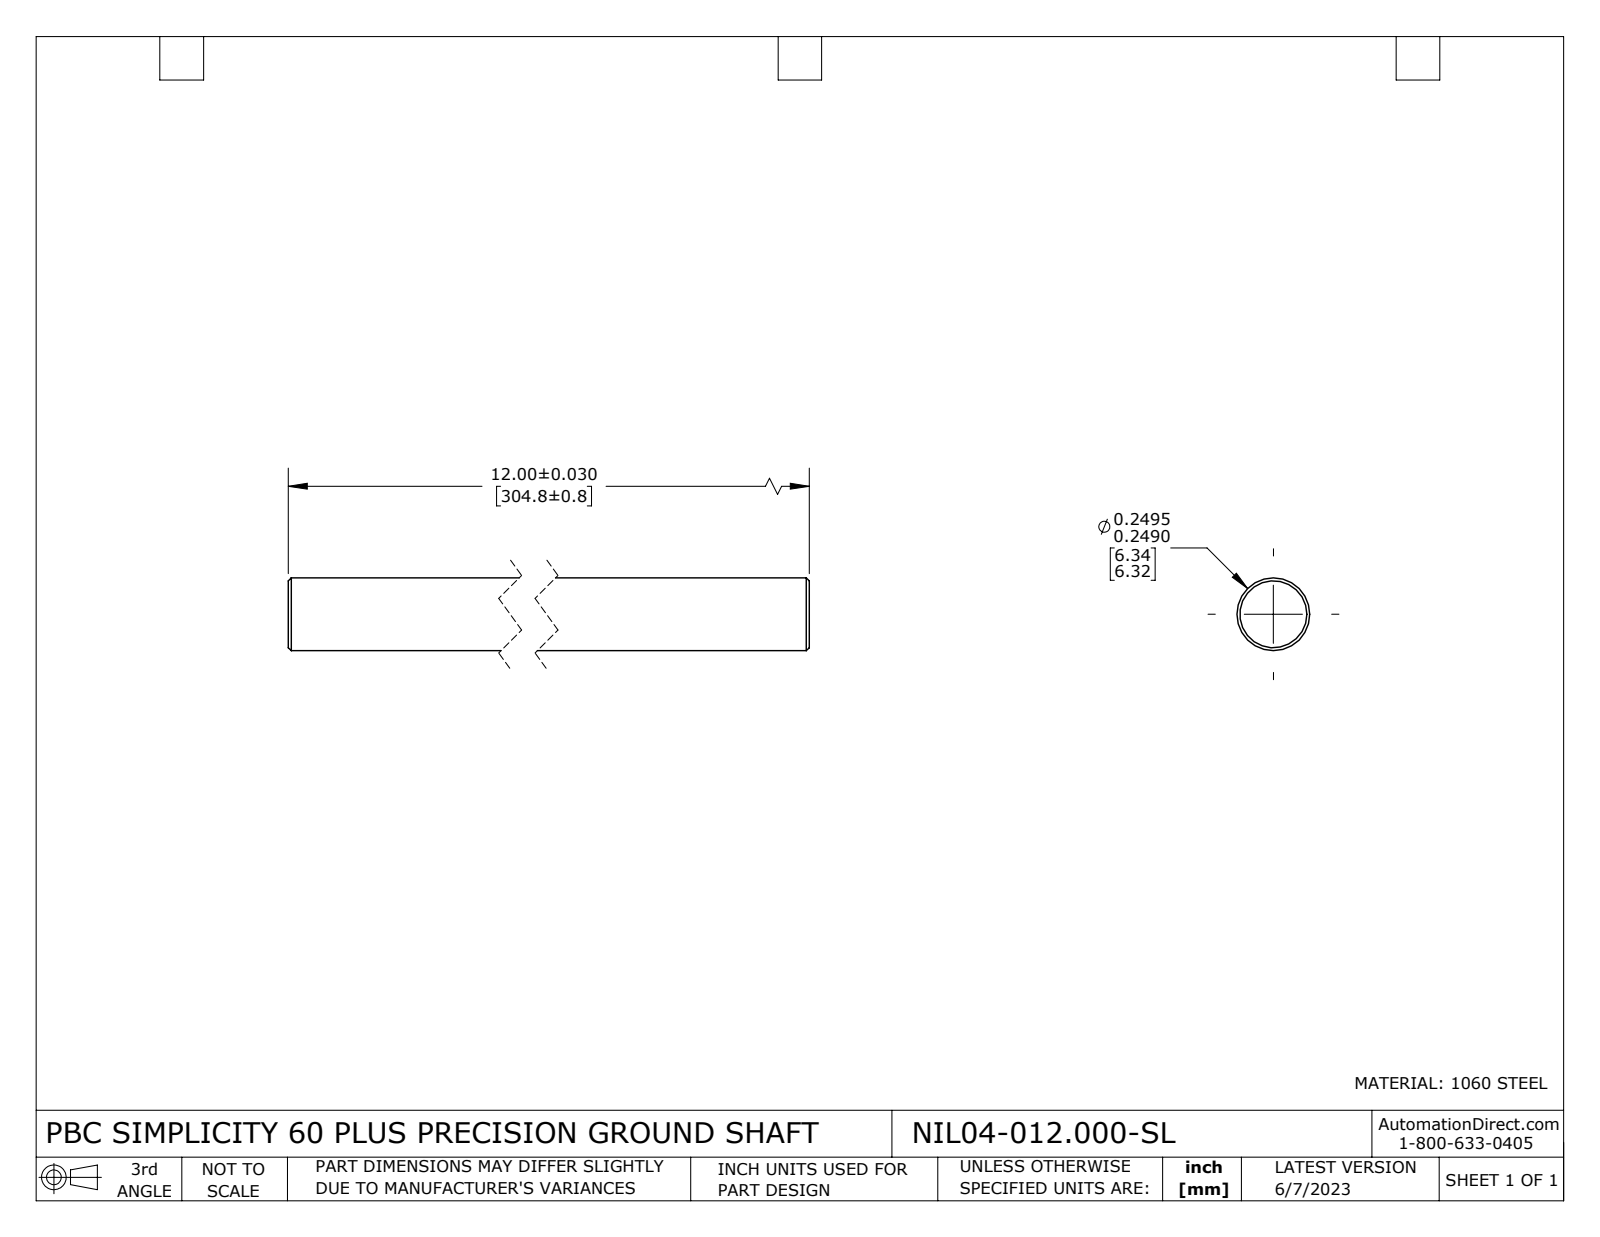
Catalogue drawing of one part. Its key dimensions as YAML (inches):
part_name: "NIL04-012.000-SL"
step_written_by: "SolidWorks 2021 (CONFIG_CONTROL_DESIGN)"
units: inches
bodies: {solids: 1, faces: 8, planar: 2, cylindrical: 2, other: 4}
overall_size: [12, 0.25, 0.25]
volume: 0.589
surface_area: 9.513
round_bosses_or_shafts:
  - {diameter: 0.25, count: 1}
face_to_face_distances: [12]
